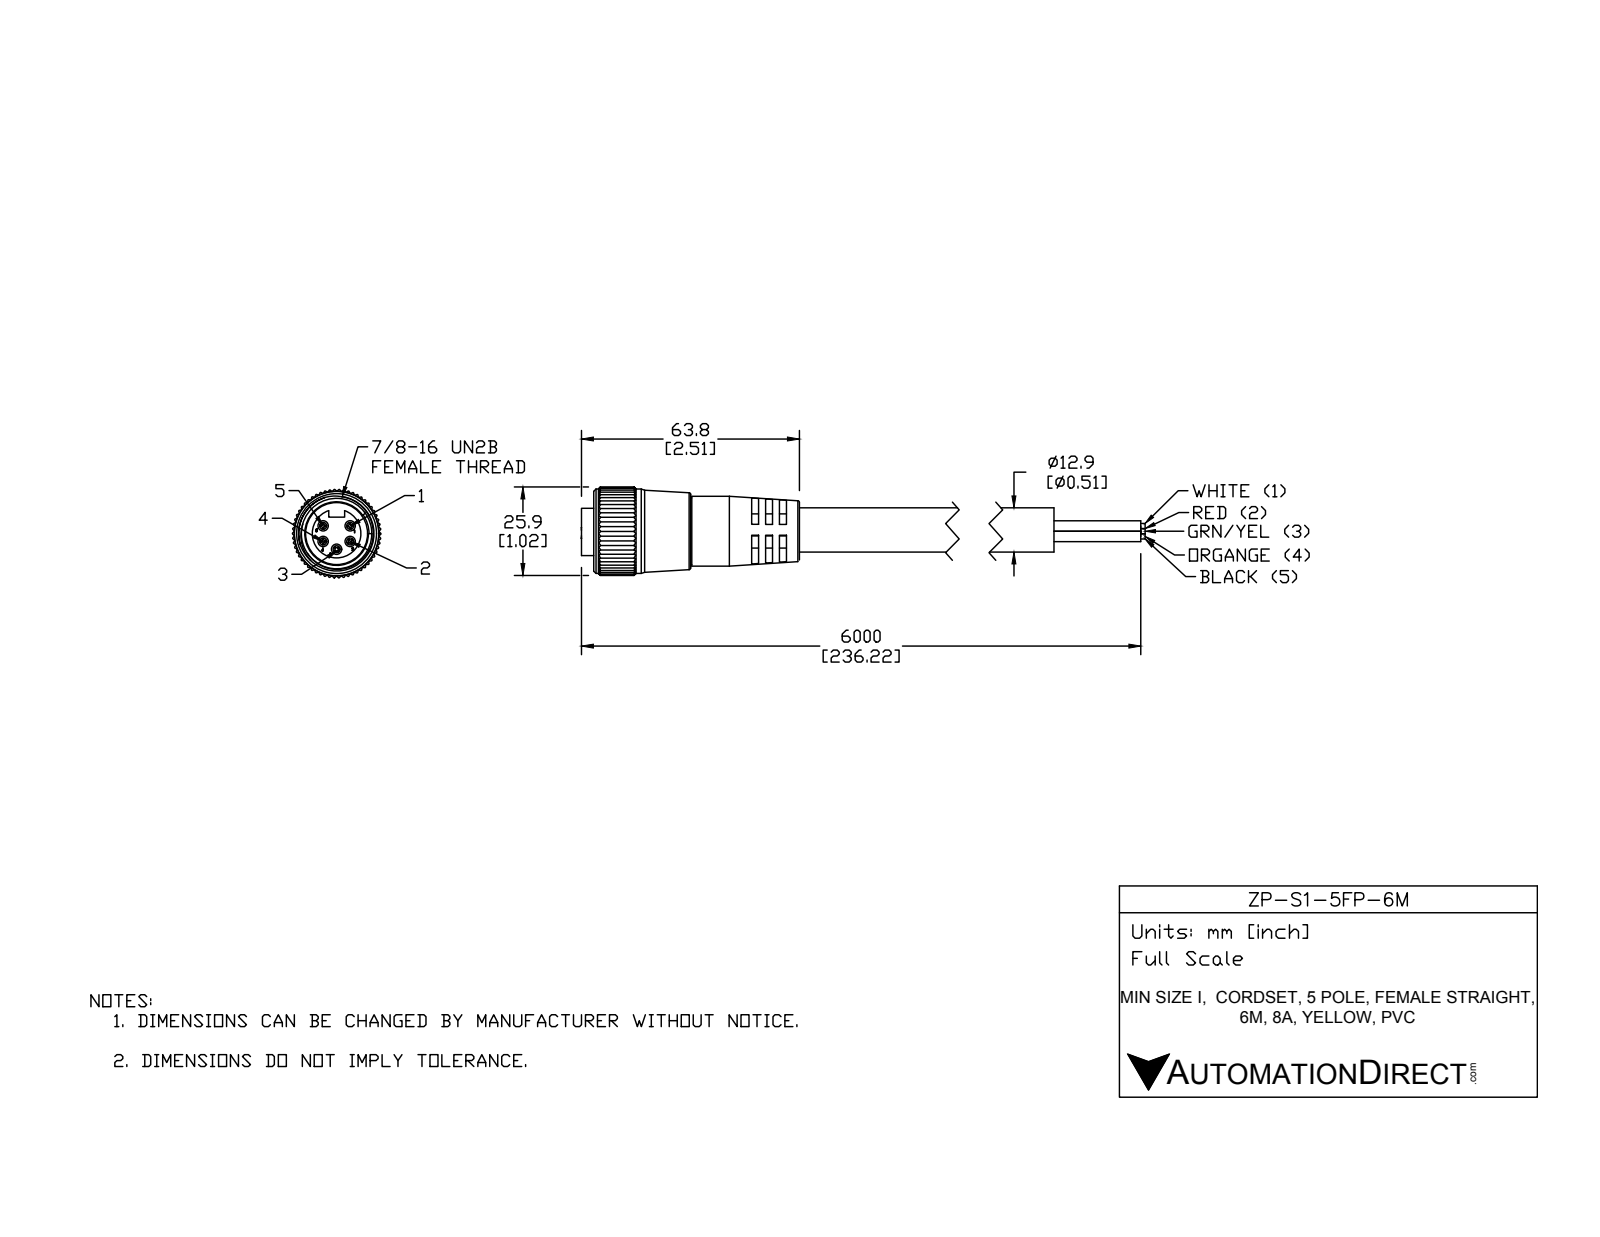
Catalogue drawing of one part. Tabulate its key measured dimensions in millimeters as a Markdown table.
| quantity | value |
| --- | --- |
| part name | ZP-S1-5FP-6M |
| STEP written by | SolidWorks 2015 (AUTOMOTIVE_DESIGN) |
| units | millimeters |
| bodies | 2 solids, 576 faces (216 planar, 310 cylindrical, 50 other) |
| overall size | 110.22 × 52.91 × 25.84 |
| volume | 30 601 mm³ |
| surface area | 12 523 mm² |
| round holes (diameter × count) | 3.05 × 5, 18.14 × 1, 20.58 × 1, 21 × 1 |
| round bosses / shafts (diameter × count) | 12.93 × 2, 24.68 × 1, 20.4 × 1, 19.5 × 1, 14.22 × 1 |
| partial cylindrical surfaces (radius × count) | 0.25 × 165, 5.25 × 1, 12.93 × 1 |
| main face-to-face distances | 4.03, 2, 2.03, 6.03, 8.06, 6.06, 21.13, 23.13, 25.16, 27.16 |
| hole center spacings | 4.57, 7.92, 4.58, 9.15 |
